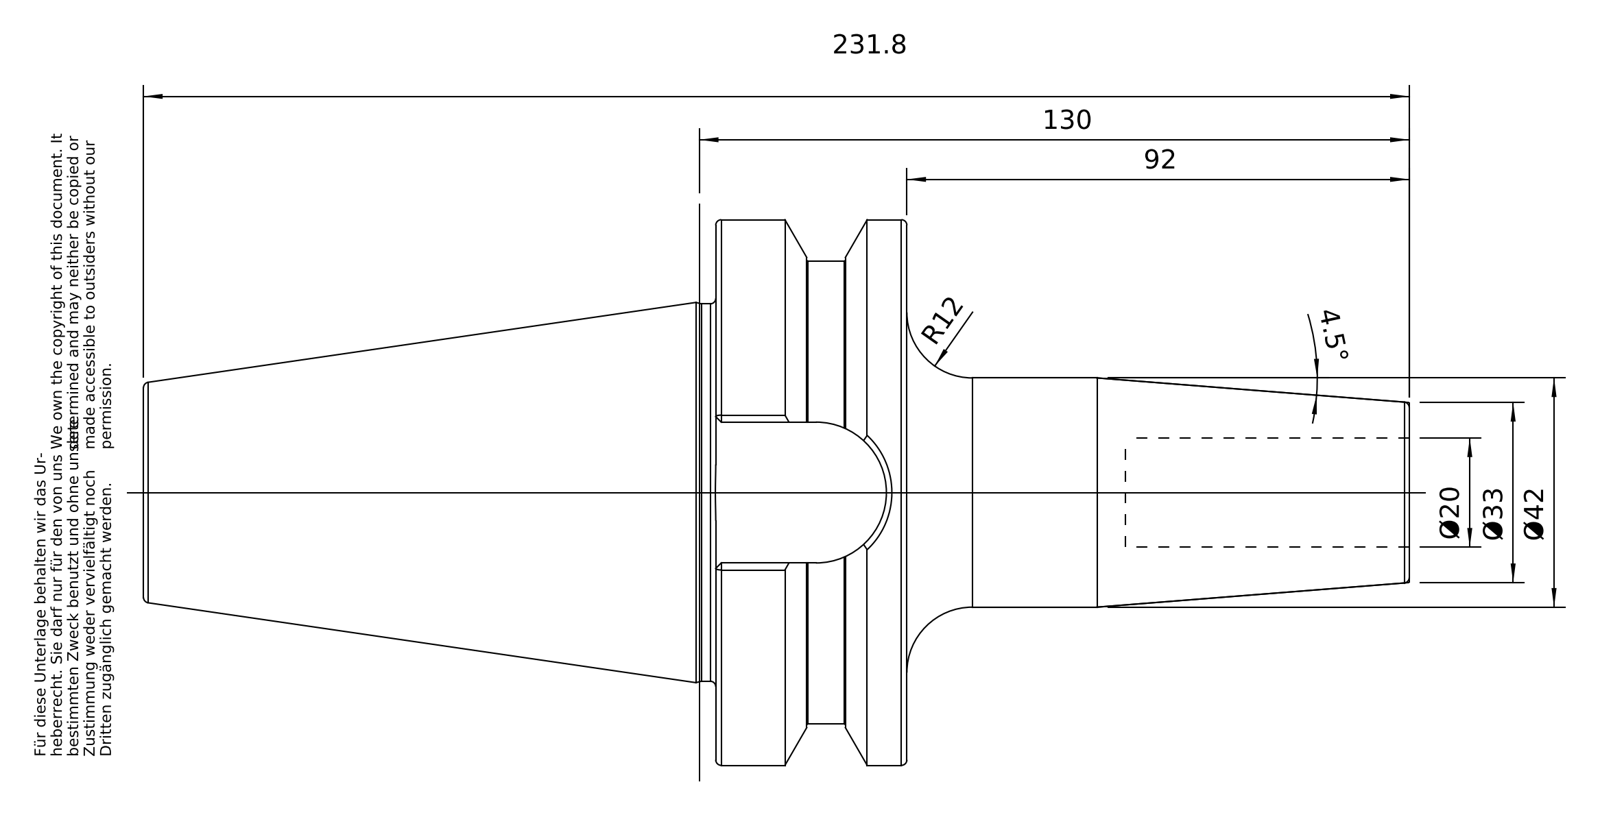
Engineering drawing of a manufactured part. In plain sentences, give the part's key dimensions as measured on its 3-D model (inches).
The part is named "50-644-20". Its 3-D file was written by "PRO/ENGINEER BY PARAMETRIC TECHNOLOGY CORPORATION, 2010430 (CONFIG_CONTROL_DESIGN)". It is 1 solid with 96 faces: 26 planar, 22 cylindrical and 48 other. Overall it measures 9.126 by 3.936 by 3.936 inches. Its volume is 34.66 cubic inches and its surface area 101.2 square inches. Round holes: 1 of diameter 0.787, 1 of diameter 0.817, 1 of diameter 0.985, 1 of diameter 1.012. Round bosses or shafts: 1 of diameter 3.936, 1 of diameter 3.337, 1 of diameter 2.722, 1 of diameter 1.654, 1 of diameter 0.945. Partial cylindrical surfaces (rounded edges, fillets, slot ends): 1 of radius 0.508. The main face-to-face distances are 1.378, 2.772, 4.126, 5.504, 9.126, 5, 3.622, 1.016, 7.079, 2.953.
